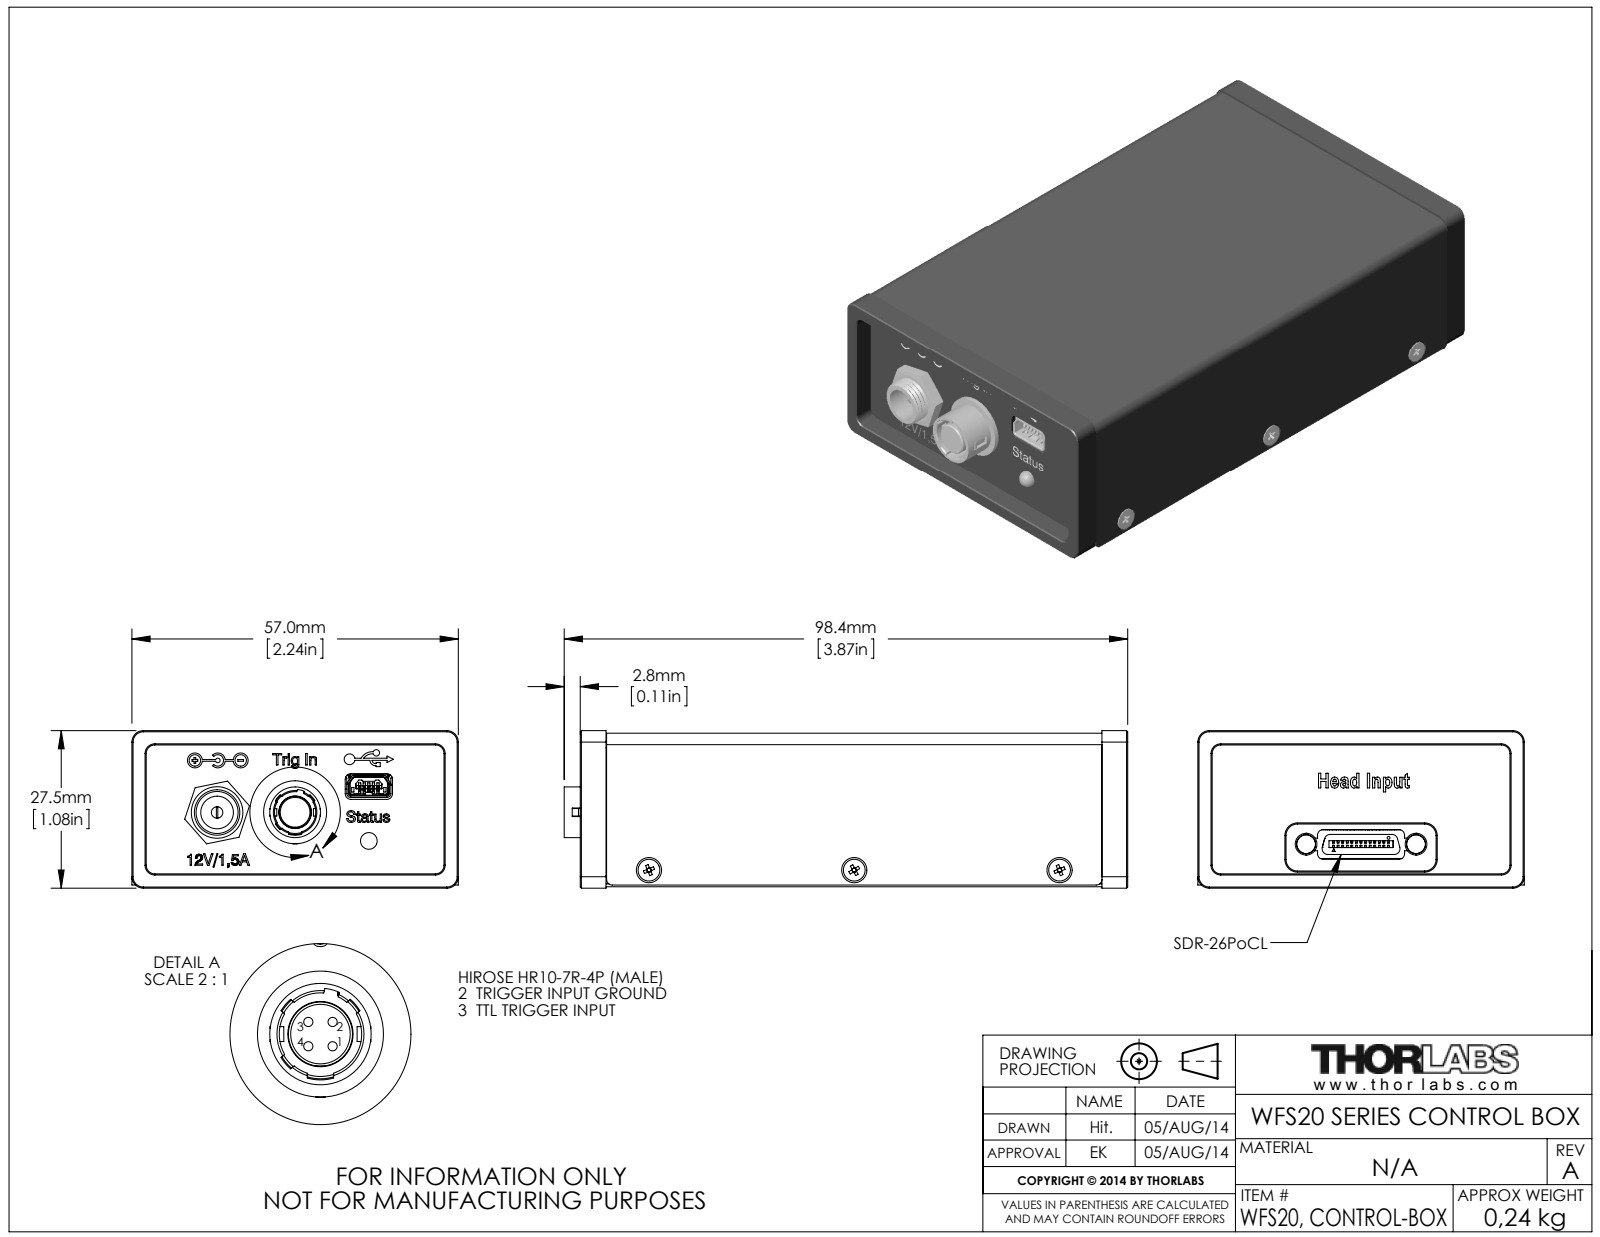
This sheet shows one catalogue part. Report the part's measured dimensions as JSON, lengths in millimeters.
{"part_name": "countersunk flat head cross recess screw_din_ISO 7046-1 - M2 x 4 - Z --- 4N; CAM907_565790576; CAM906R01_X1_1; HR10-7R-4S (+8 more)", "step_written_by": "SolidWorks 2014 (AUTOMOTIVE_DESIGN)", "units": "millimeters", "bodies": {"solids": 21, "faces": 2864, "planar": 1733, "cylindrical": 675, "other": 456}, "overall_size": [98.4, 57, 27.5], "volume_mm3": 74434, "surface_area_mm2": 74397, "round_holes": [[0.8, 7], [1.6, 6], [2.05, 6], [2.7, 6], [0.7, 4], [1.2, 4], [2.3, 4], [1, 2], [1.8, 2], [2.2, 2], [2.6, 2], [5.7, 2]], "round_bosses_or_shafts": [[5.5, 6], [2, 6], [1.2, 6], [3.8, 5], [11, 2], [6.5, 2], [3, 2], [9.4, 1]], "partial_cylinders_radius": [[2, 68], [0.12, 40], [1, 19], [1.5, 17], [0.15, 14], [0.2, 14], [0.3, 14], [4.1, 12]], "face_to_face_distances": [1, 8, 9.53, 11.53, 5.53, 7.27, 10, 5.5, 26.8, 25.8], "hole_center_spacings": [1.6, 2.26, 12.41, 19.2, 31.6, 1.5, 44, 57]}
